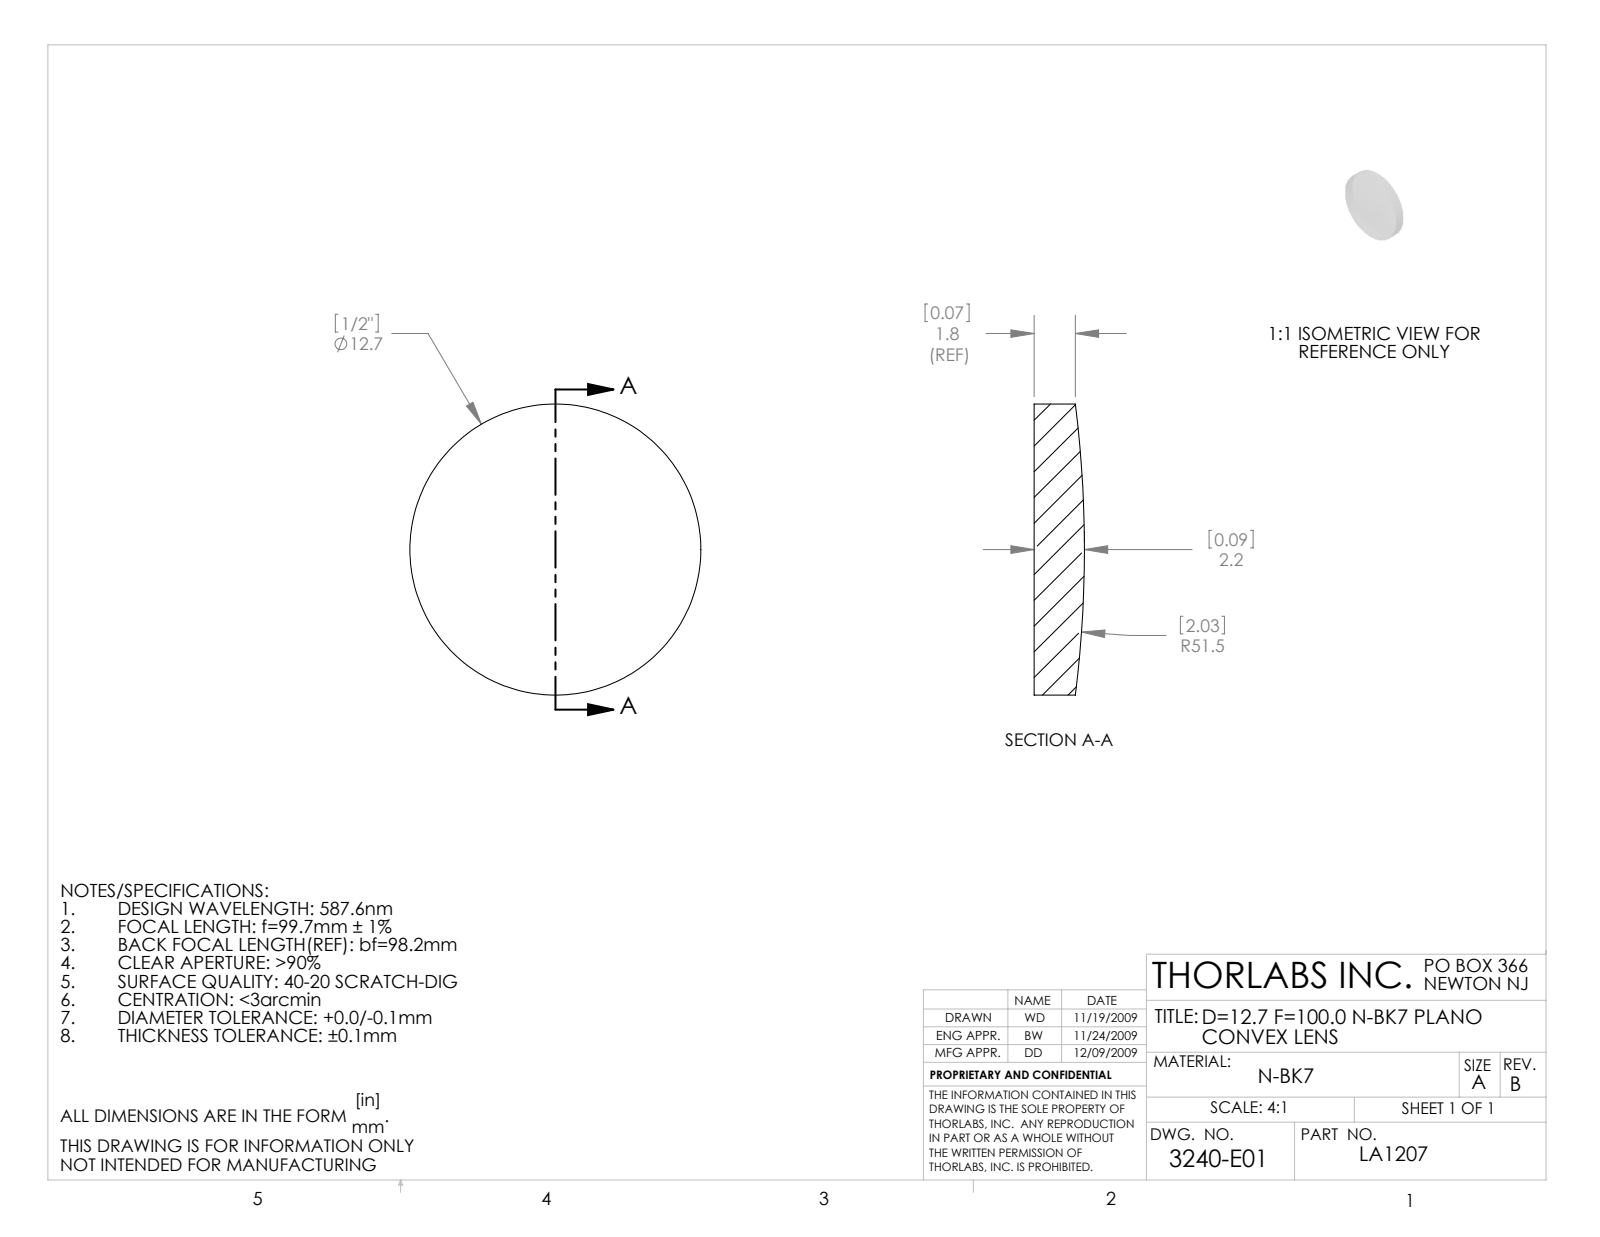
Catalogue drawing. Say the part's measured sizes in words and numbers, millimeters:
The part is named "3240-E0W". Its 3-D file was written by "SolidWorks 2009 (AUTOMOTIVE_DESIGN)". It is 1 solid with 5 faces: 1 planar, 2 cylindrical and 2 other. Overall it measures 12.7 by 12.7 by 2.19 millimeters. Its volume is 253 cubic millimeters and its surface area 326 square millimeters. Round bosses or shafts: 1 of diameter 12.7.
